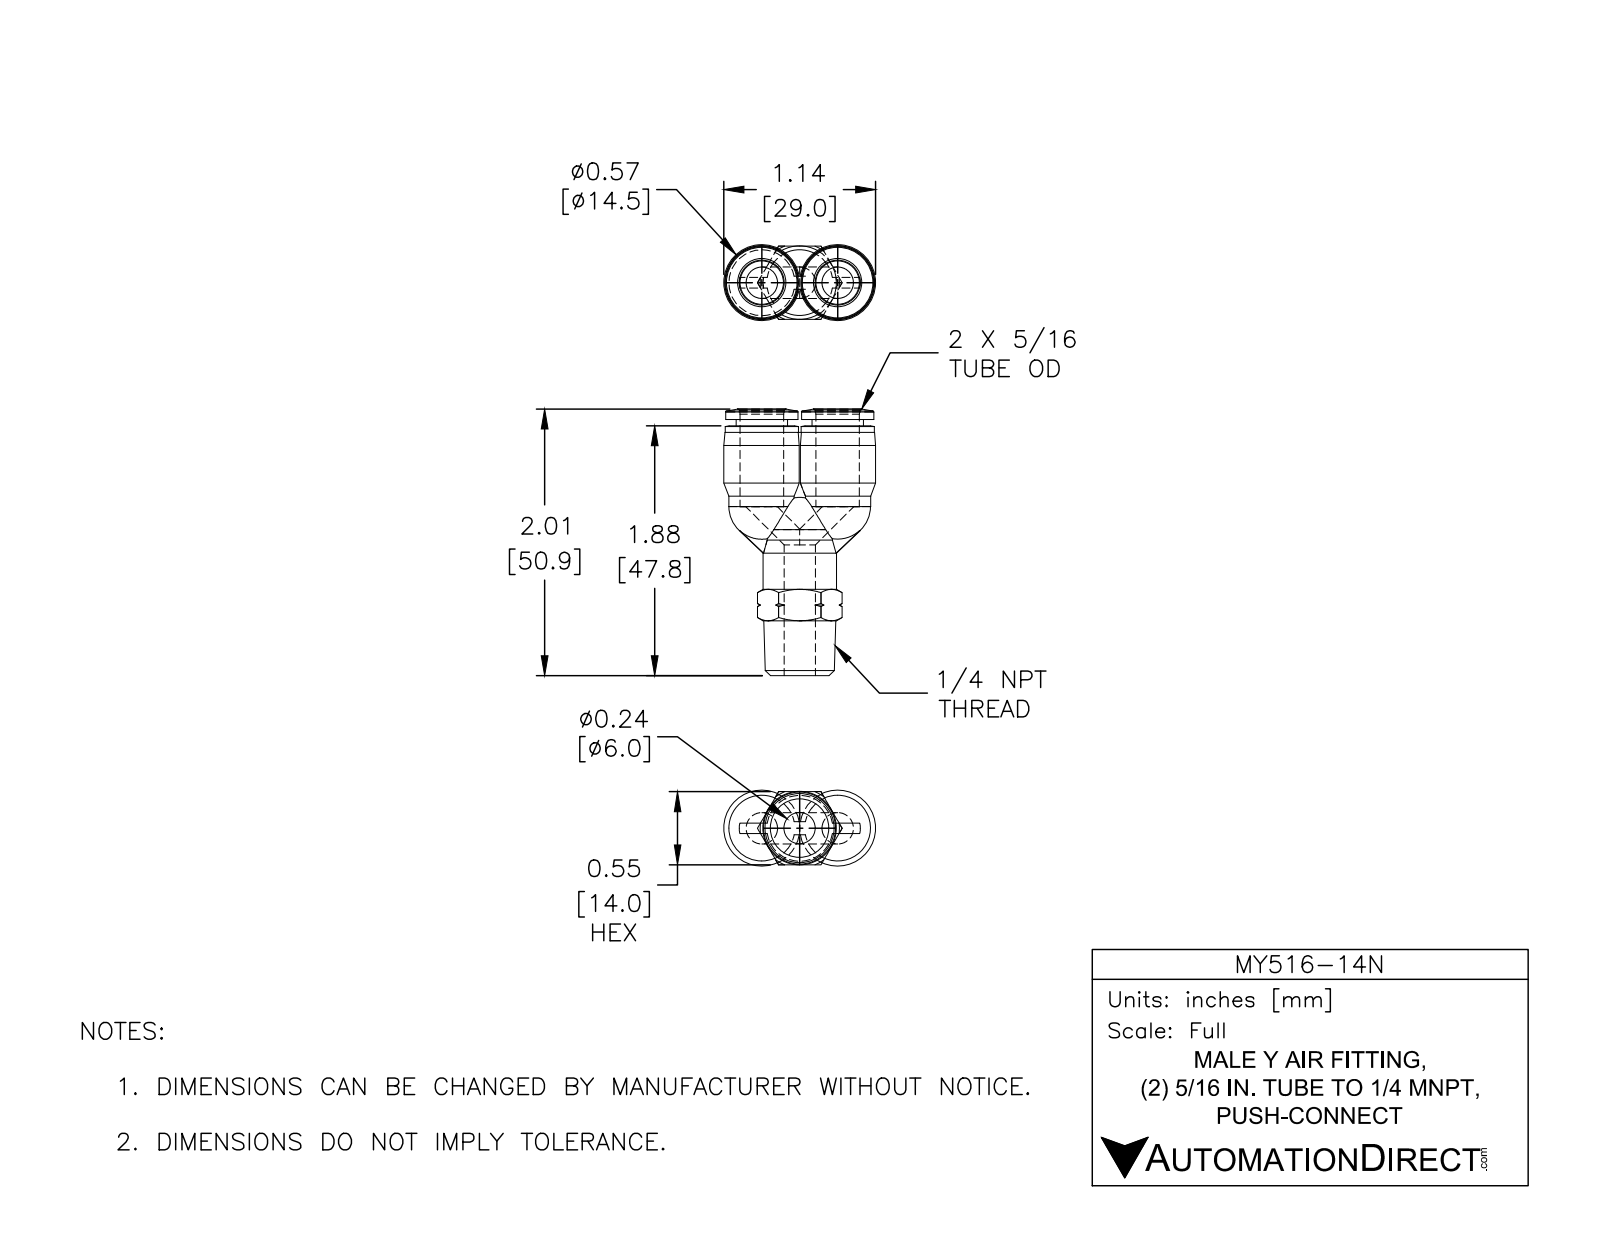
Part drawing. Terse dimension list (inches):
name: MY516-14N
written by: SolidWorks 2015 (CONFIG_CONTROL_DESIGN)
unit: in
bodies: 1 solid, 126 faces (21 planar, 31 cylindrical, 74 other)
size: 2.006 × 1.142 × 0.571
volume: 0.48 in³; area: 8.613 in²
holes: 2× ⌀0.327, 1× ⌀0.236
bosses: 3× ⌀0.551, 3× ⌀0.496, 2× ⌀0.571, 2× ⌀0.543, 2× ⌀0.386
face distances: 0.551, 0.047, 1.88, 1.927, 1.27, 0.61, 0.657, 0.236, 0.315, 0.226
hole spacings: 0.285, 0.571
